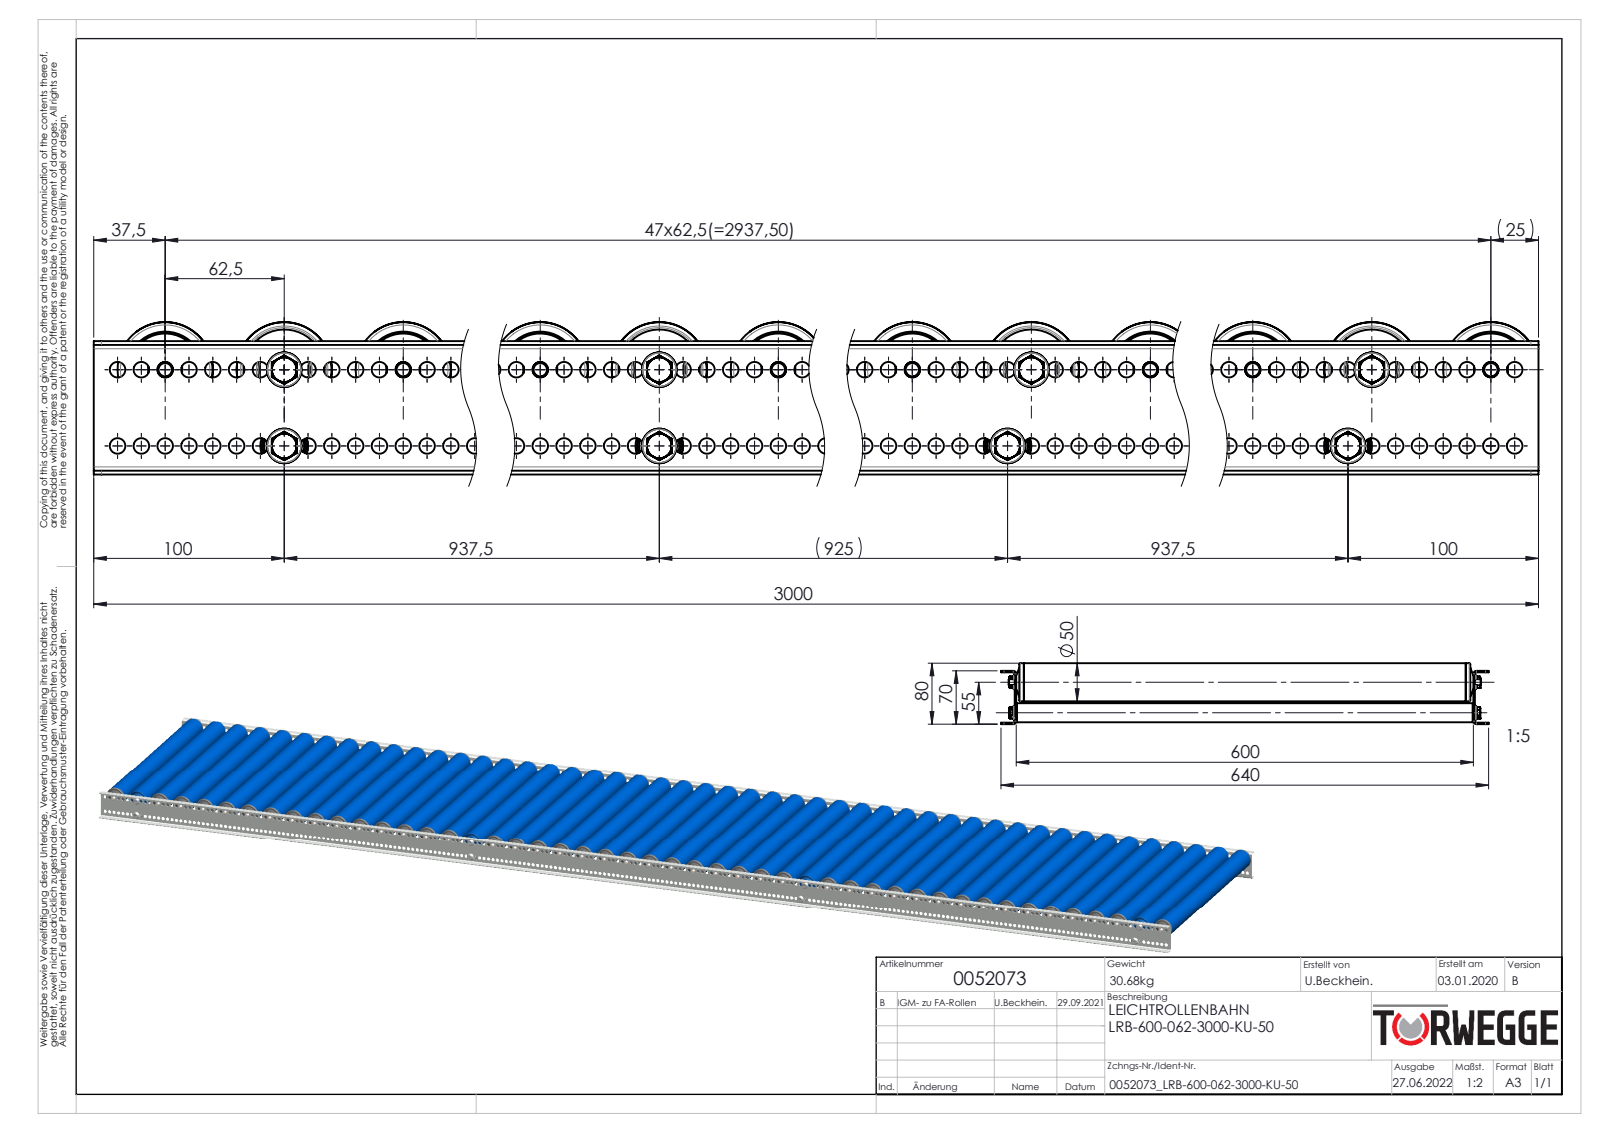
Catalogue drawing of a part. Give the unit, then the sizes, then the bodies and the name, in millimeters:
Units: millimetres
Overall size (bounding box): 3000 × 640 × 80
Round holes (diameter × count): ⌀8.2 ×478, ⌀7.6 ×44, ⌀8 ×44, ⌀25 ×44, ⌀30 ×44, ⌀35 ×44, ⌀39.4 ×44, ⌀40 ×44, ⌀6.8 ×8, ⌀12 ×4, ⌀12.1 ×4, ⌀16 ×4
Round bosses / shafts (diameter × count): ⌀50 ×48, ⌀44.4 ×44, ⌀38 ×44, ⌀36 ×44, ⌀33 ×44, ⌀22 ×44, ⌀21 ×44, ⌀25 ×8
Partial cylindrical surfaces — rounded edges, fillets, slot ends (radius × count): R0.6 ×88, R0.75 ×88, R2.45 ×88, R4.87 ×44, R7 ×44, R2.5 ×16, R4 ×8, R2 ×4
Main face-to-face distances: 2, 602, 68, 600, 604, 592, 70, 66, 12, 6
Hole centre spacings: 12.5, 25, 37.5, 50, 62.5, 75, 87.5, 100
Volume: 17 370 000 mm³ · Surface area: 12 660 000 mm²
Bodies: 722 solids, 13708 faces (3468 planar, 6424 cylindrical, 3816 other)
Part name (STEP PRODUCT): KUT100-50x2,8-KB-A8-FA_KFG_0034516_KUT100-50x2,8-KB-A8-FA-EL=600; Profil_LRB-20x70x20x2_KFG_S109080_U-PROFIL-20-70-20-2-LRB-L=3000; 0026267_Typ-KUT100-50x2,8-8_Lageboden-schematisch; 0039778-Achse-ST-Ø08-KFG_AL620-G (+8 more)
STEP written by: SolidWorks 2020 (AUTOMOTIVE_DESIGN)
